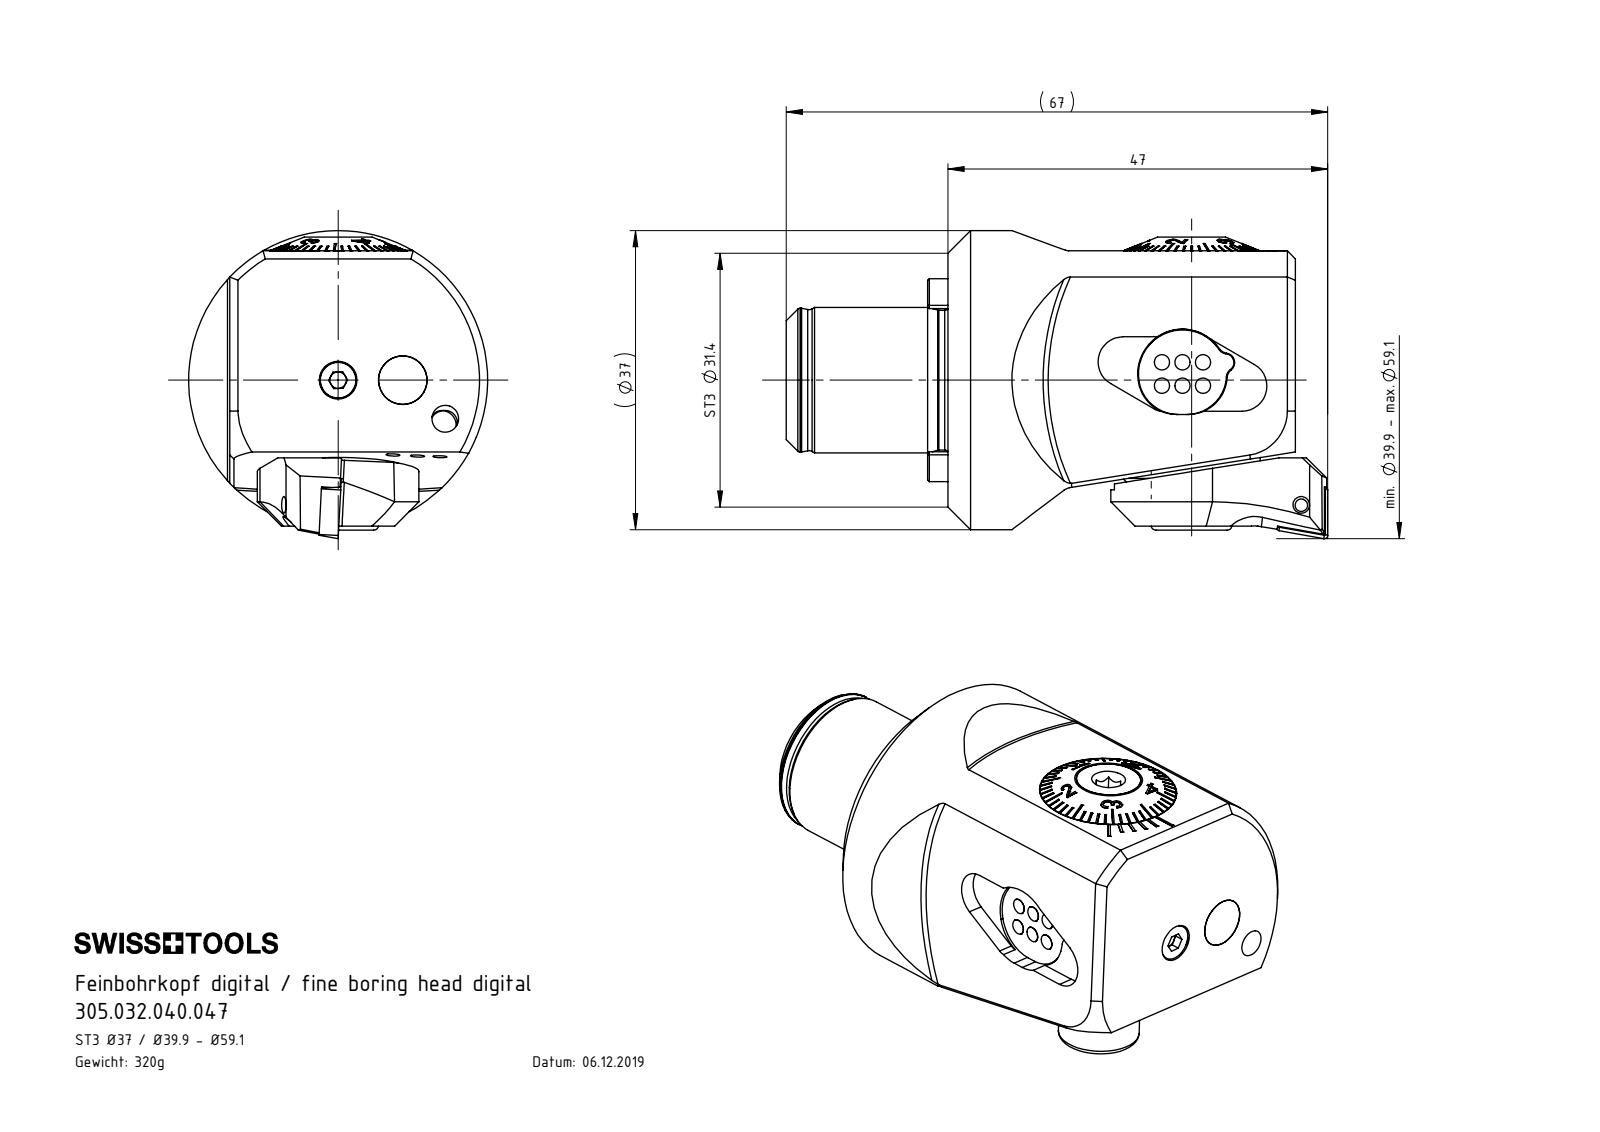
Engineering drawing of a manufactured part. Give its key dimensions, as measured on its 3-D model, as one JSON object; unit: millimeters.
{"part_name": "PEE-DA1.011.026_A; F32-BG2.009.012_A; Klebstoff D6; F32-BG2.017.004_A (+8 more)", "step_written_by": "SolidWorks 2017 (CONFIG_CONTROL_DESIGN)", "units": "millimeters", "bodies": {"solids": 22, "faces": 961, "planar": 396, "cylindrical": 217, "other": 348}, "overall_size": [67, 35.15, 32], "volume_mm3": 35201, "surface_area_mm2": 17890, "round_holes": [[2.5, 5], [2.8, 3], [2.05, 2], [5, 2], [0.7, 1], [2.1, 1], [2.7, 1], [2.9, 1], [3, 1], [3.3, 1], [3.85, 1], [6, 1]], "round_bosses_or_shafts": [[1.9, 6], [6, 2], [2.5, 2], [32, 1], [18, 1], [17.8, 1], [17.3, 1], [16.98, 1]], "partial_cylinders_radius": [[0.5, 8], [0.21, 6], [0.36, 5], [1.1, 3], [1.2, 3], [1.75, 2], [2.6, 2], [2.73, 2]], "face_to_face_distances": [43, 4.5, 25.35, 20.85, 5.5, 1.5, 3.7, 0.8, 24.55, 26.35], "hole_center_spacings": [10.85, 13.48, 37.9, 2.6, 2.84, 3.84, 3.99, 5.7]}
